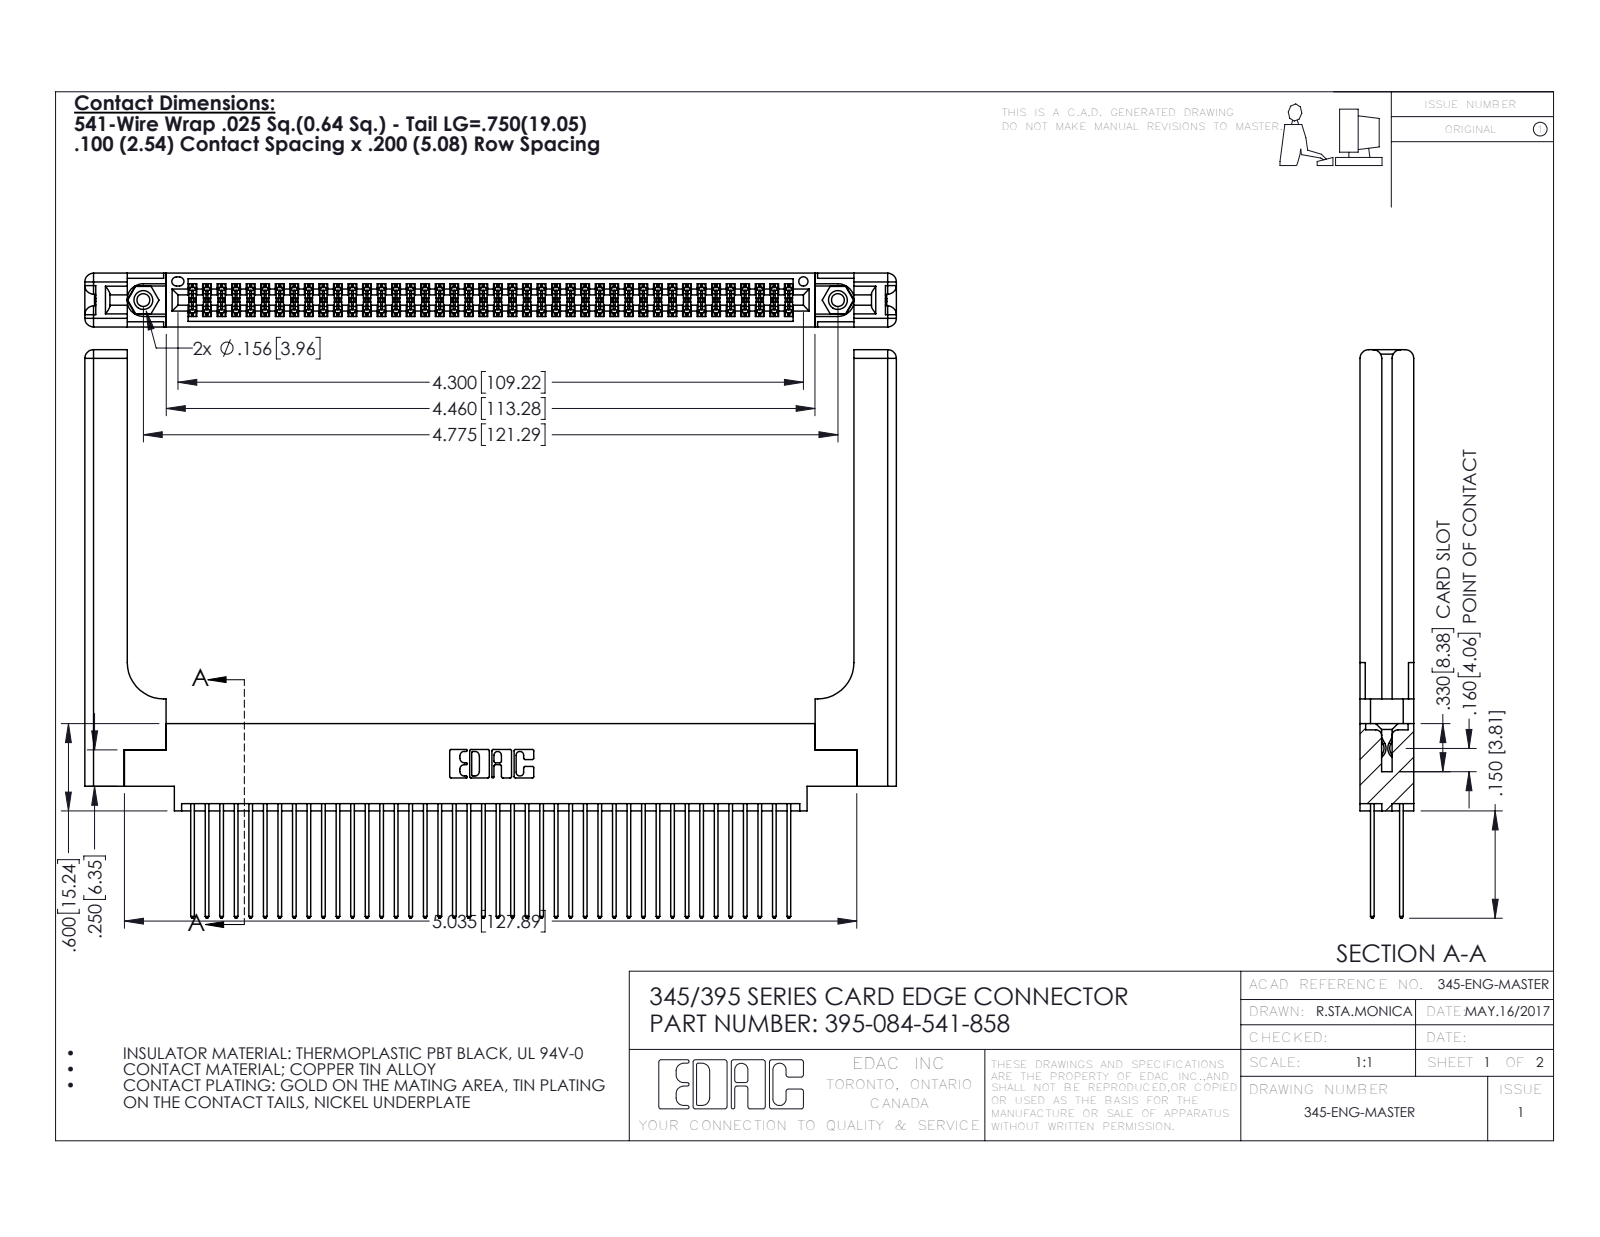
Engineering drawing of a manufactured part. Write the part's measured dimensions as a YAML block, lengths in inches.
part_name: "345-250-001_345-250-001-102; 345-292-001_345-293-141; 395-084-541-858; 345-220-058_345-220-058 (+1 more)"
step_written_by: "SolidWorks 2016 (CONFIG_CONTROL_DESIGN)"
units: inches
bodies: {solids: 89, faces: 4586, planar: 3004, cylindrical: 1522, other: 60}
overall_size: [5.579, 3.907, 0.37]
volume: 1.38
surface_area: 43.96
round_holes:
  - {diameter: 0.089, count: 2}
  - {diameter: 0.125, count: 2}
  - {diameter: 0.156, count: 2}
  - {diameter: 0.064, count: 1}
round_bosses_or_shafts:
  - {diameter: 0.155, count: 2}
partial_cylinders:
  - {radius: 0.006, count: 126}
  - {radius: 0.01, count: 84}
  - {radius: 0.01, count: 22}
  - {radius: 0.06, count: 16}
  - {radius: 0.007, count: 6}
  - {radius: 0.031, count: 6}
  - {radius: 0.026, count: 3}
  - {radius: 0.014, count: 2}
face_to_face_distances: [0.072, 0.298, 0.37, 0.098, 0.272, 0.025, 0.2, 0.225, 0.175, 0.148]
hole_center_spacings: [0.27, 4.539, 4.775]
